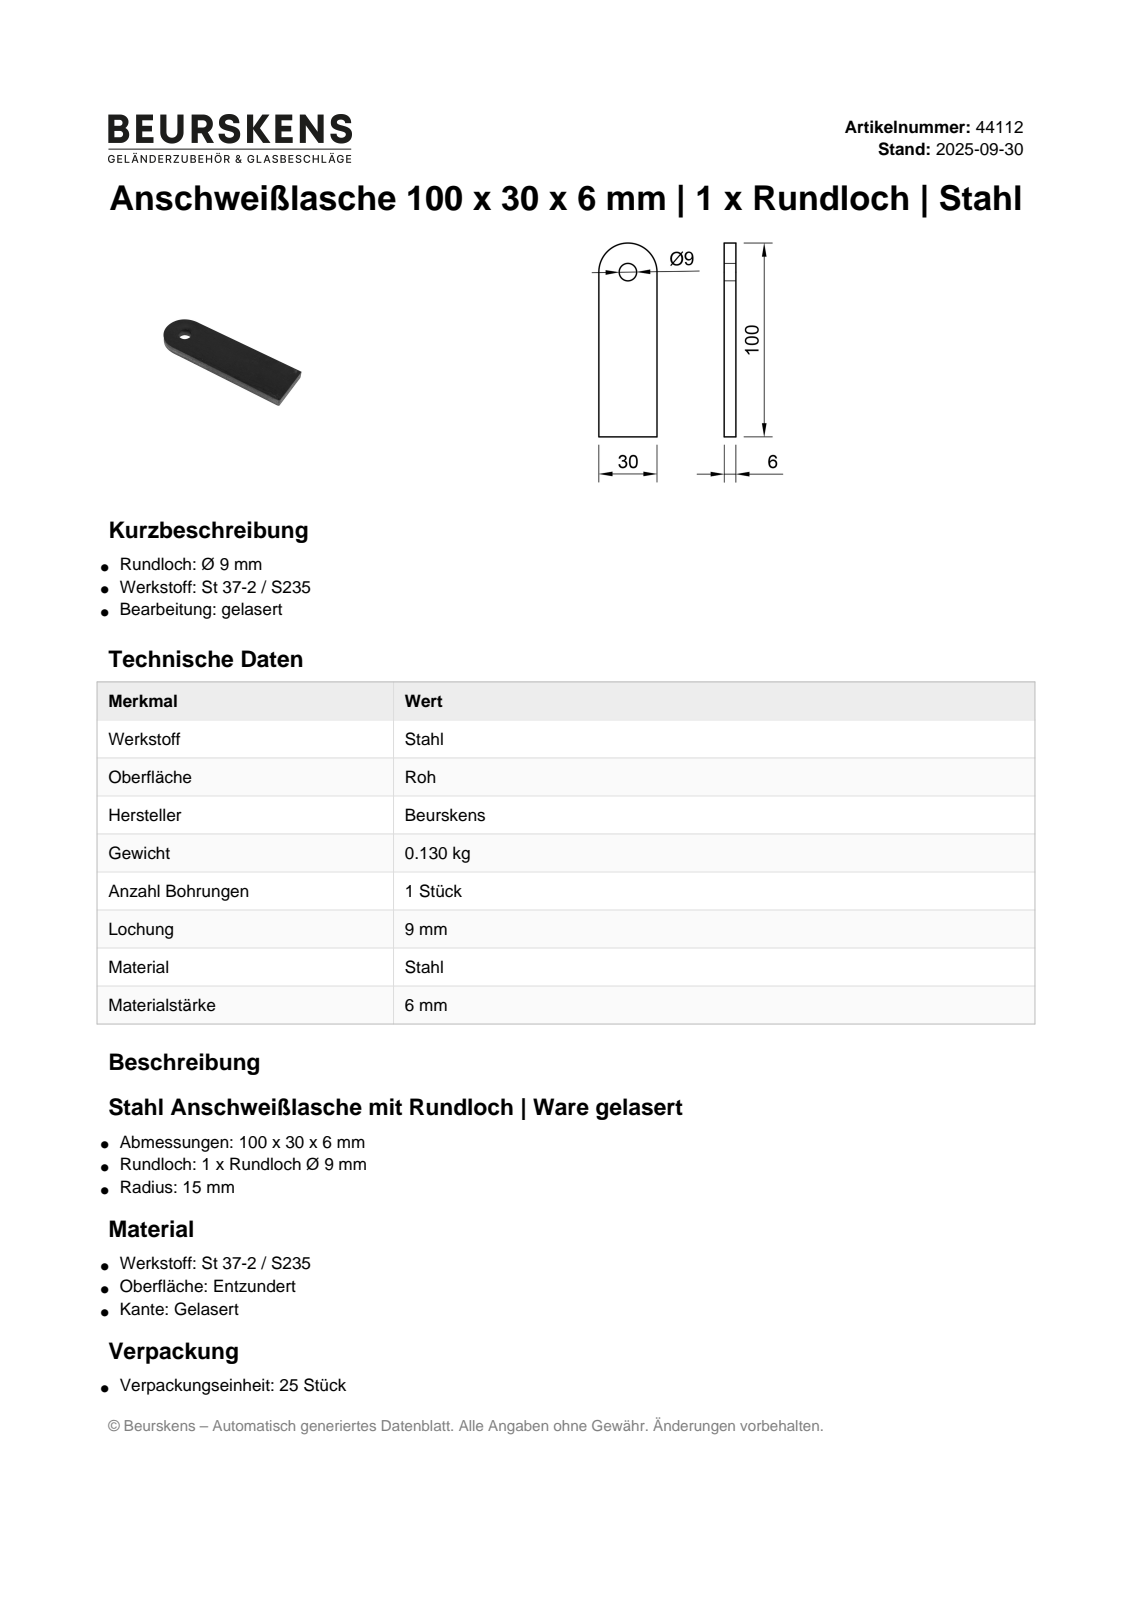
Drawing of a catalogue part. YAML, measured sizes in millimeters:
part_name: "44112"
step_written_by: "Autodesk Inventor 2023 (AUTOMOTIVE_DESIGN)"
units: millimeters
bodies: {solids: 1, faces: 7, planar: 5, cylindrical: 2, other: 0}
overall_size: [100, 30, 6]
volume: 17039
surface_area: 7332
round_holes:
  - {diameter: 9, count: 1}
partial_cylinders:
  - {radius: 15, count: 1}
face_to_face_distances: [6, 30]
